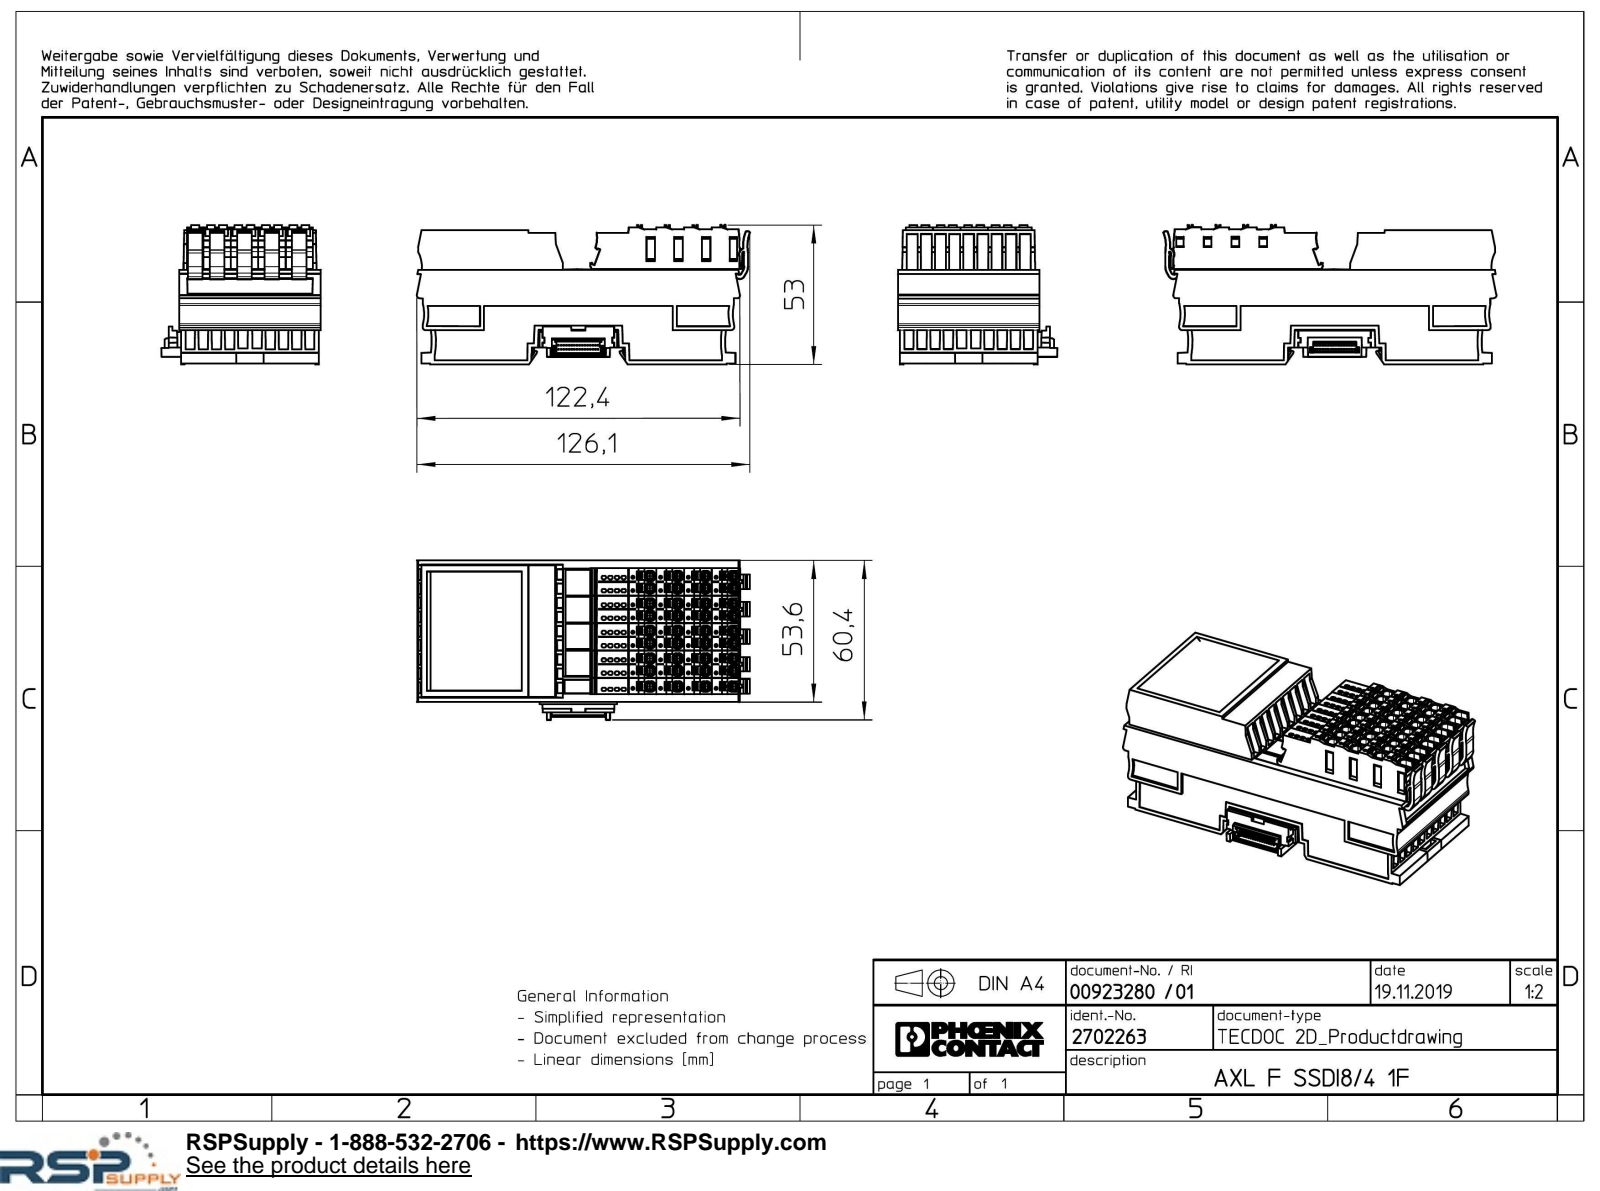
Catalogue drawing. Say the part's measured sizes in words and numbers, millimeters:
The part is named "FIBO_F_YE1018-select; AXL_BE_SCHILD_F1-select; AXL_F_BS_F-select; FIBO_COLOR_CODE_BU5012-select (+7 more)". Its 3-D file was written by "Creo Elements/Direct Modeling 20.1A 29-Sep-2018 (C) Parametric Technology GmbH (AUTOMOTIVE_DESIGN)". It is 13 solids with 5109 faces: 4231 planar, 656 cylindrical and 222 other. Overall it measures 126.17 by 60.4 by 52.77 millimeters. Its volume is 273 525 cubic millimeters and its surface area 85 651 square millimeters. Round holes: 36 of diameter 1.2. Partial cylindrical surfaces (rounded edges, fillets, slot ends): 147 of radius 0.5, 130 of radius 1.5, 36 of radius 1.25, 8 of radius 1, 6 of radius 12.6, 5 of radius 0.3, 5 of radius 3, 2 of radius 0.17. The main face-to-face distances are 10.4, 20.8, 10.5, 52.7, 0.9, 31.2, 10.3, 35.45, 20.7, 13.25. The hole center spacings are 14.78, 10.4, 10.5, 11.63, 23.3, 23.43, 11.81, 18.64.
